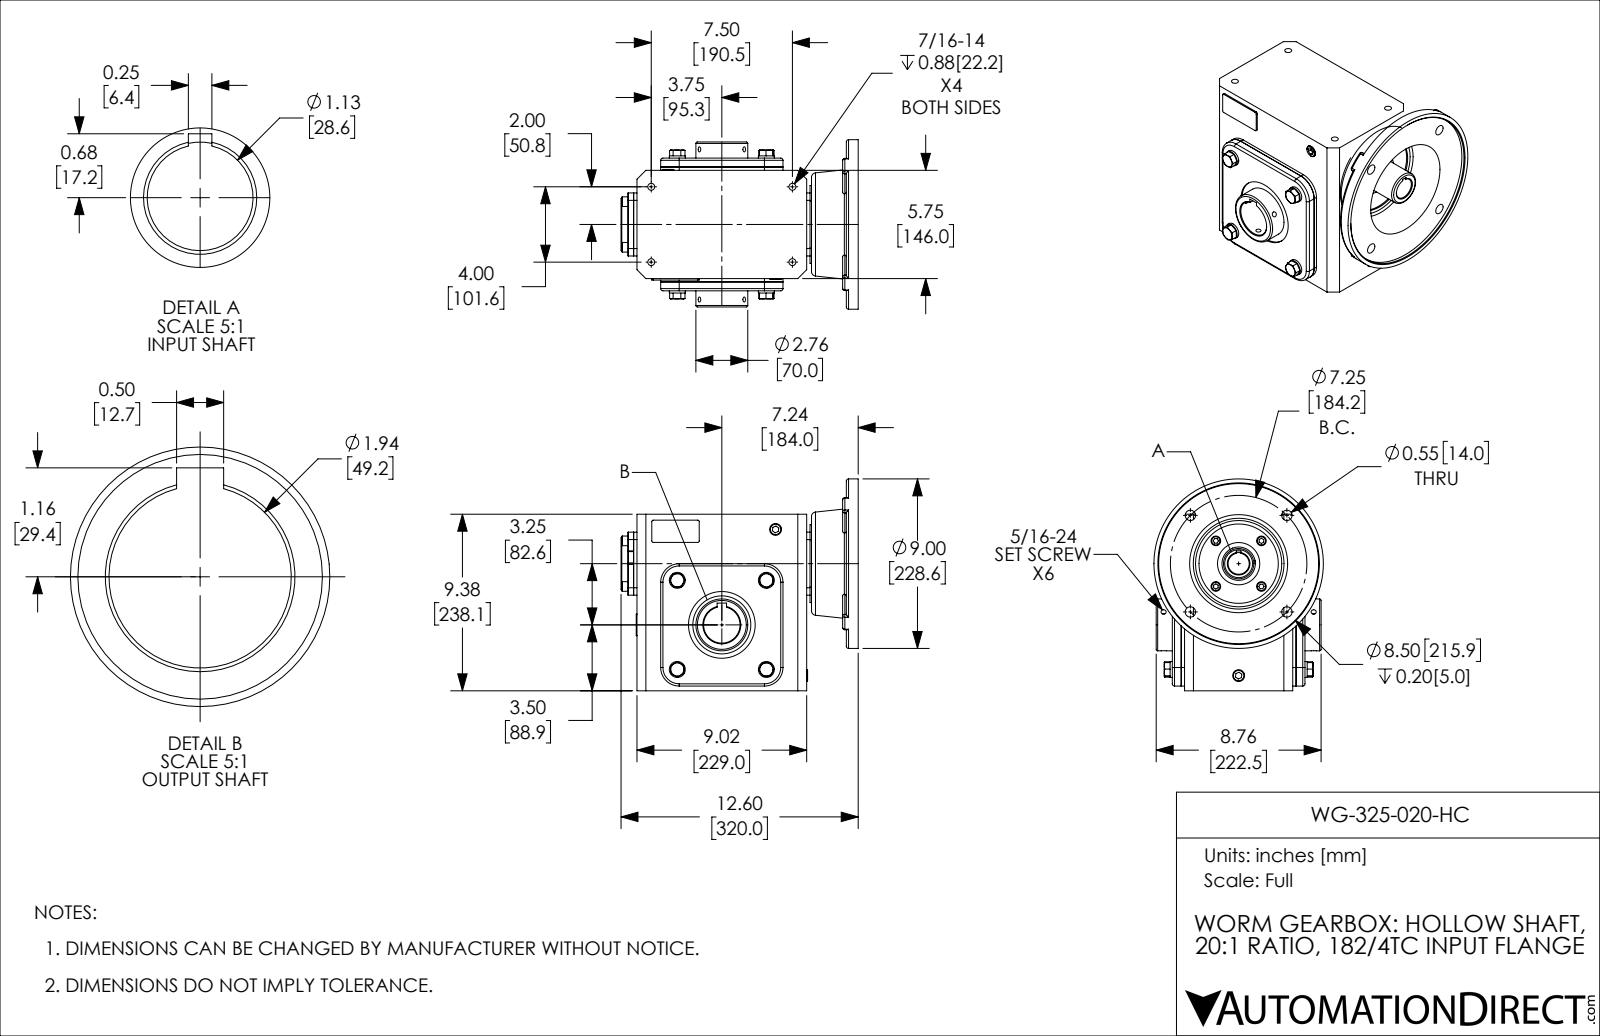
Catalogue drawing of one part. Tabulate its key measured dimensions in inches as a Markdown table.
| quantity | value |
| --- | --- |
| part name | WG-325-020-HC |
| STEP written by | SolidWorks 2017 (AUTOMOTIVE_DESIGN) |
| units | inches |
| bodies | 40 solids, 665 faces (332 planar, 206 cylindrical, 127 other) |
| overall size | 12.598 × 11.25 × 9 |
| volume | 542 in³ |
| surface area | 1 111 in² |
| round holes (diameter × count) | 0.272 × 6, 0.354 × 4, 0.368 × 4, 0.551 × 4, 0.628 × 3, 0.591 × 1, 0.978 × 1, 1.125 × 1, 1.181 × 1, 1.937 × 1, 2.244 × 1, 2.441 × 1 |
| round bosses / shafts (diameter × count) | 0.846 × 4, 0.512 × 4, 9 × 1, 4.134 × 1, 2.835 × 1, 1.772 × 1, 1.142 × 1 |
| partial cylindrical surfaces (radius × count) | 0.118 × 18, 0.079 × 7, 0.394 × 4, 0.906 × 4, 0.984 × 4, 0.02 × 2, 0.039 × 2 |
| main face-to-face distances | 0.079, 0.177, 6.496, 0.394, 0.571, 6.319, 5.925, 6.398, 0.65, 0.472 |
| hole center spacings | 4.009, 1.713, 1.913, 2.422, 3.625, 4.244, 5.127, 5.338 |
